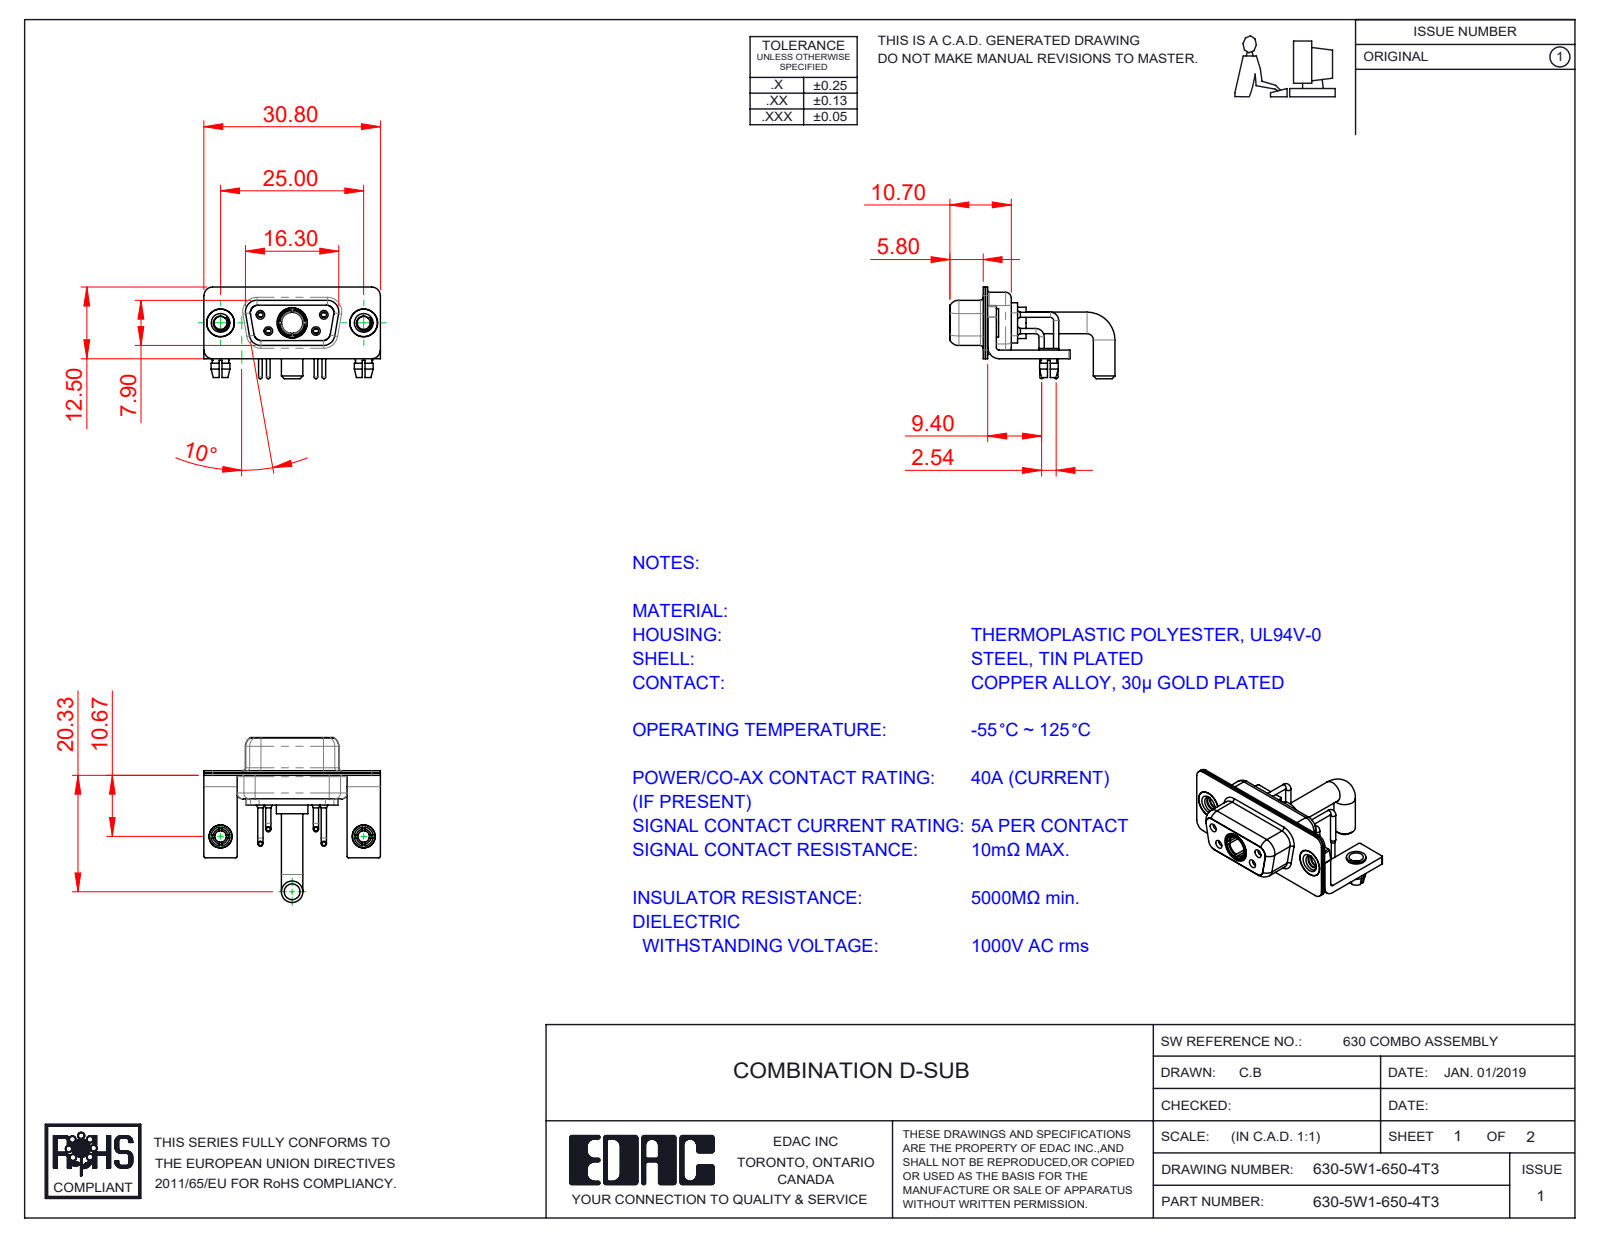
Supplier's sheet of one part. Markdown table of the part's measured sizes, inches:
| quantity | value |
| --- | --- |
| part name | 630Combo Housing_5W1; 630Combo Threaded Rivet_3; 630Combo Contact Row 1; 630Combo Contact Row 2 (+6 more) |
| STEP written by | SolidWorks 2020 (CONFIG_CONTROL_DESIGN) |
| units | inches |
| bodies | 15 solids, 701 faces (224 planar, 304 cylindrical, 173 other) |
| overall size | 1.213 × 1.134 × 0.63 |
| volume | 0.138 in³ |
| surface area | 8.238 in² |
| round holes (diameter × count) | 0.079 × 6, 0.035 × 4, 0.043 × 4, 0.059 × 4, 0.191 × 3, 0.063 × 2, 0.067 × 2, 0.089 × 2, 0.098 × 2, 0.126 × 2, 0.157 × 2, 0.159 × 2 |
| round bosses / shafts (diameter × count) | 0.035 × 4, 0.026 × 4, 0.197 × 2, 0.195 × 2, 0.189 × 2, 0.157 × 2, 0.148 × 2, 0.134 × 2 |
| partial cylindrical surfaces (radius × count) | 0.01 × 16, 0.059 × 16, 0.079 × 13, 0.053 × 8, 0.063 × 8, 0.02 × 5, 0.024 × 4, 0.026 × 4 |
| main face-to-face distances | 0.016, 0.031, 0.059, 0.055, 0.018, 0.333, 0.071, 0.091, 0.35, 0.244 |
| hole center spacings | 0.124, 0.225, 0.28, 0.492, 0.713, 0.984, 0.173, 0.173 |
